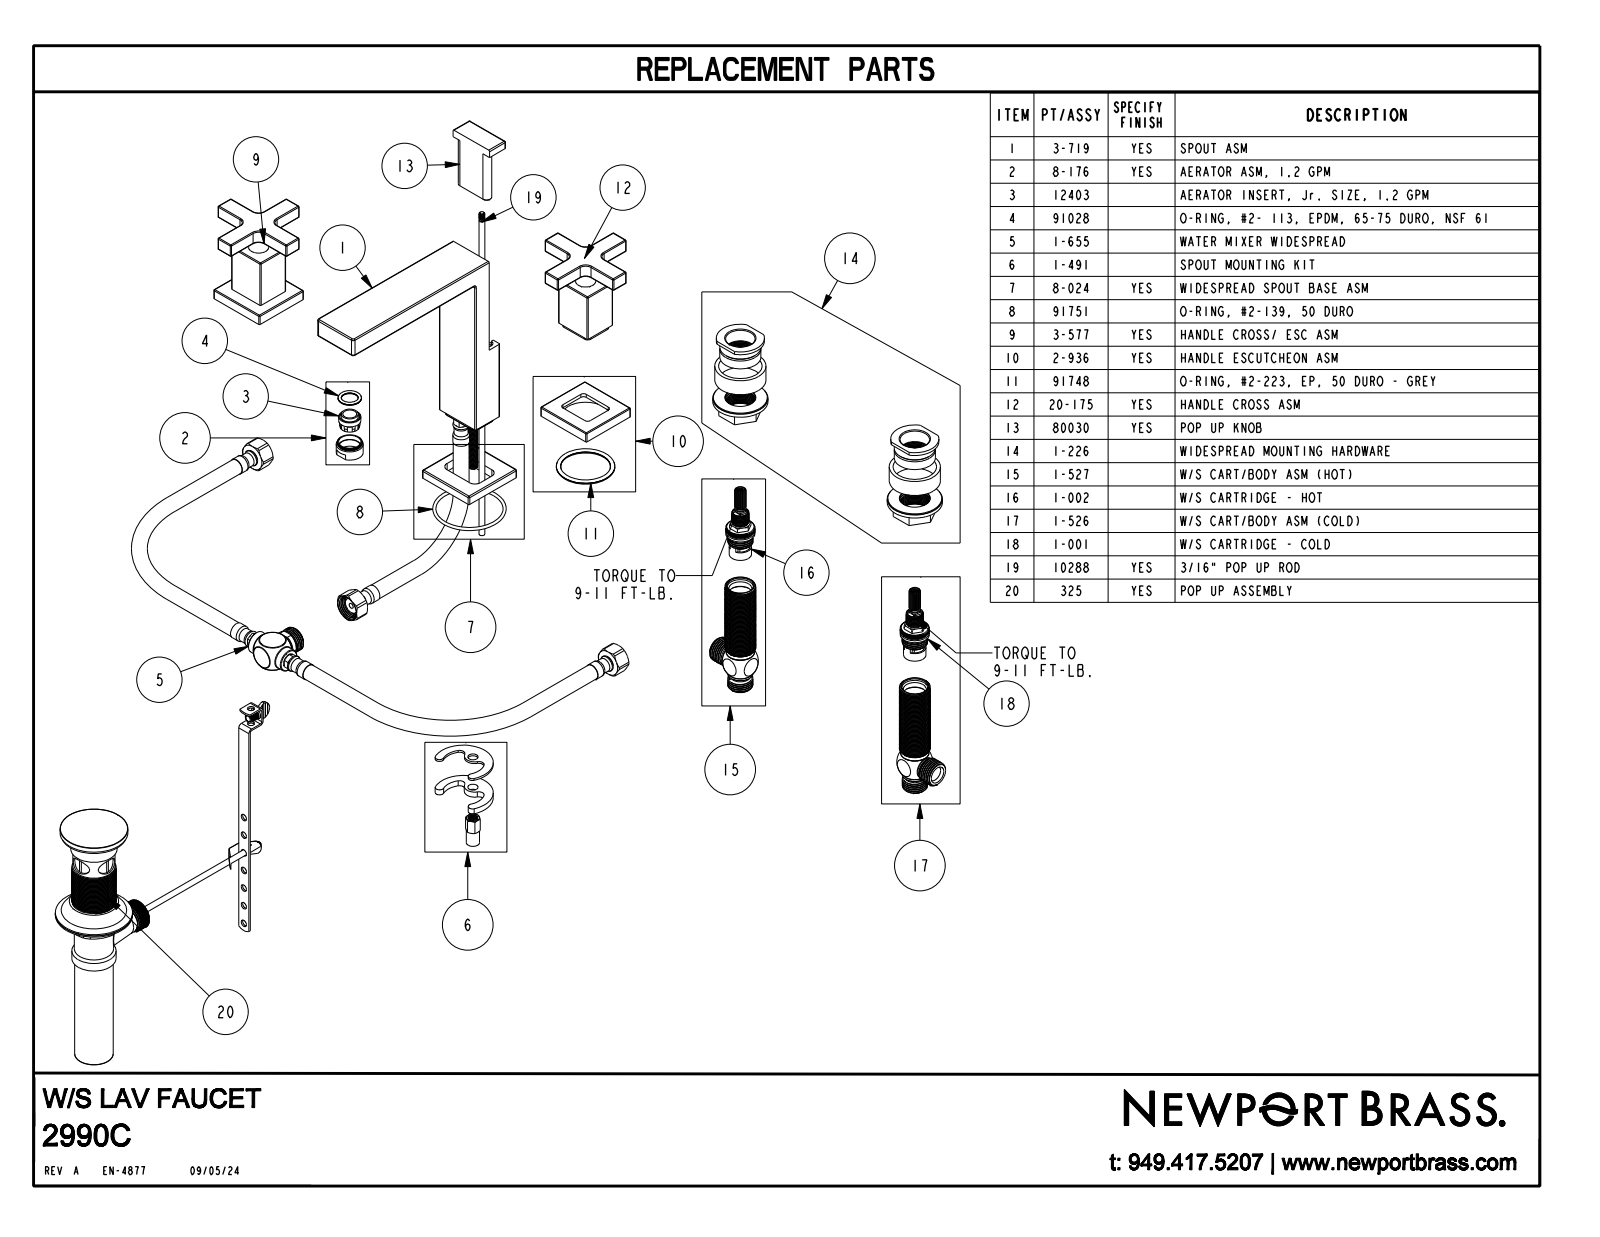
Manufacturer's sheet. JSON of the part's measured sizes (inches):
{"part_name": "2990C", "step_written_by": "CREO PARAMETRIC BY PTC INC, 2019352 (CONFIG_CONTROL_DESIGN)", "units": "inches", "bodies": {"solids": 5, "faces": 2030, "planar": 664, "cylindrical": 859, "other": 507}, "overall_size": [11.14, 8.26, 6.744], "volume_in3": 12.9, "surface_area_in2": 351.8, "round_holes": [[0.11, 2], [0.14, 2], [0.36, 2], [0.375, 2], [0.506, 2], [0.51, 2], [0.563, 2], [0.572, 2], [0.625, 2], [1.58, 2], [1.936, 2], [0.15, 1]], "round_bosses_or_shafts": [[1.899, 2], [1.64, 2], [0.65, 2], [0.523, 2], [0.433, 2], [0.4, 2], [0.383, 2], [0.28, 2]], "partial_cylinders_radius": [[0.03, 68], [0.04, 40], [0.25, 16], [0.01, 12], [0.042, 12], [0.02, 8], [0.125, 8], [0.15, 8]], "face_to_face_distances": [0.11, 1.67, 0.654, 0.519, 0.544, 8, 2.99, 3.644, 0.629, 2.696], "hole_center_spacings": [3.697, 4.321, 7.224, 0.46, 0.461, 0.54, 0.67, 0.672]}
